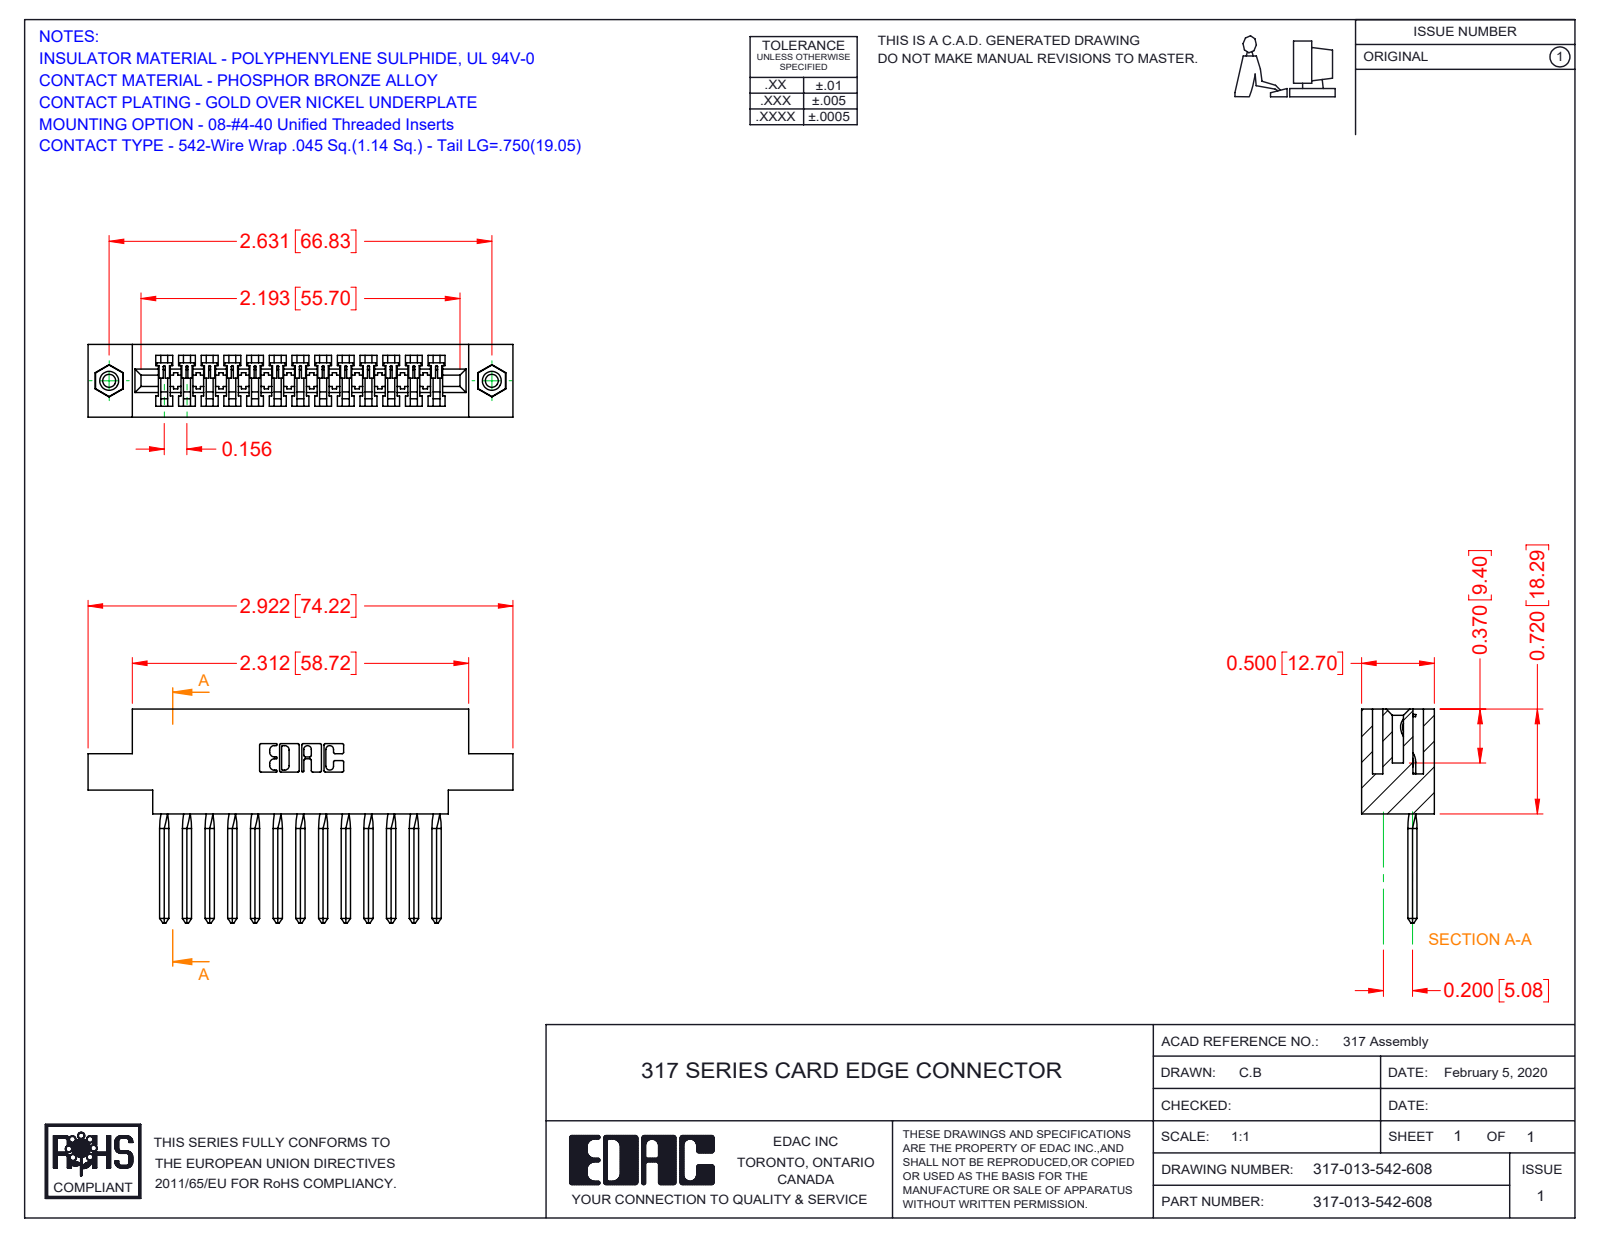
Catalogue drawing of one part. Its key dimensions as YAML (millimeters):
part_name: "317-290-003_542; 317-013-542-608; 317 Part_.156 Dia - TI; 345-250-001_345-250-003-102"
step_written_by: "SolidWorks 2016 (CONFIG_CONTROL_DESIGN)"
units: millimeters
bodies: {solids: 16, faces: 1137, planar: 922, cylindrical: 147, other: 68}
overall_size: [74.2, 37.3, 12.7]
volume: 10700
surface_area: 12410
round_holes:
  - {diameter: 2.3, count: 2}
  - {diameter: 3.2, count: 2}
  - {diameter: 4, count: 2}
round_bosses_or_shafts:
  - {diameter: 3.9, count: 2}
partial_cylinders:
  - {radius: 0.2, count: 26}
  - {radius: 0.3, count: 22}
  - {radius: 0.2, count: 6}
  - {radius: 0.8, count: 6}
  - {radius: 0.7, count: 3}
  - {radius: 1.9, count: 1}
  - {radius: 2.3, count: 1}
  - {radius: 2.5, count: 1}
face_to_face_distances: [12.7, 1.9, 10.8, 2.8, 1.7, 8.9, 5.6, 3.5, 18.3, 8.4]
hole_center_spacings: [66.8]
